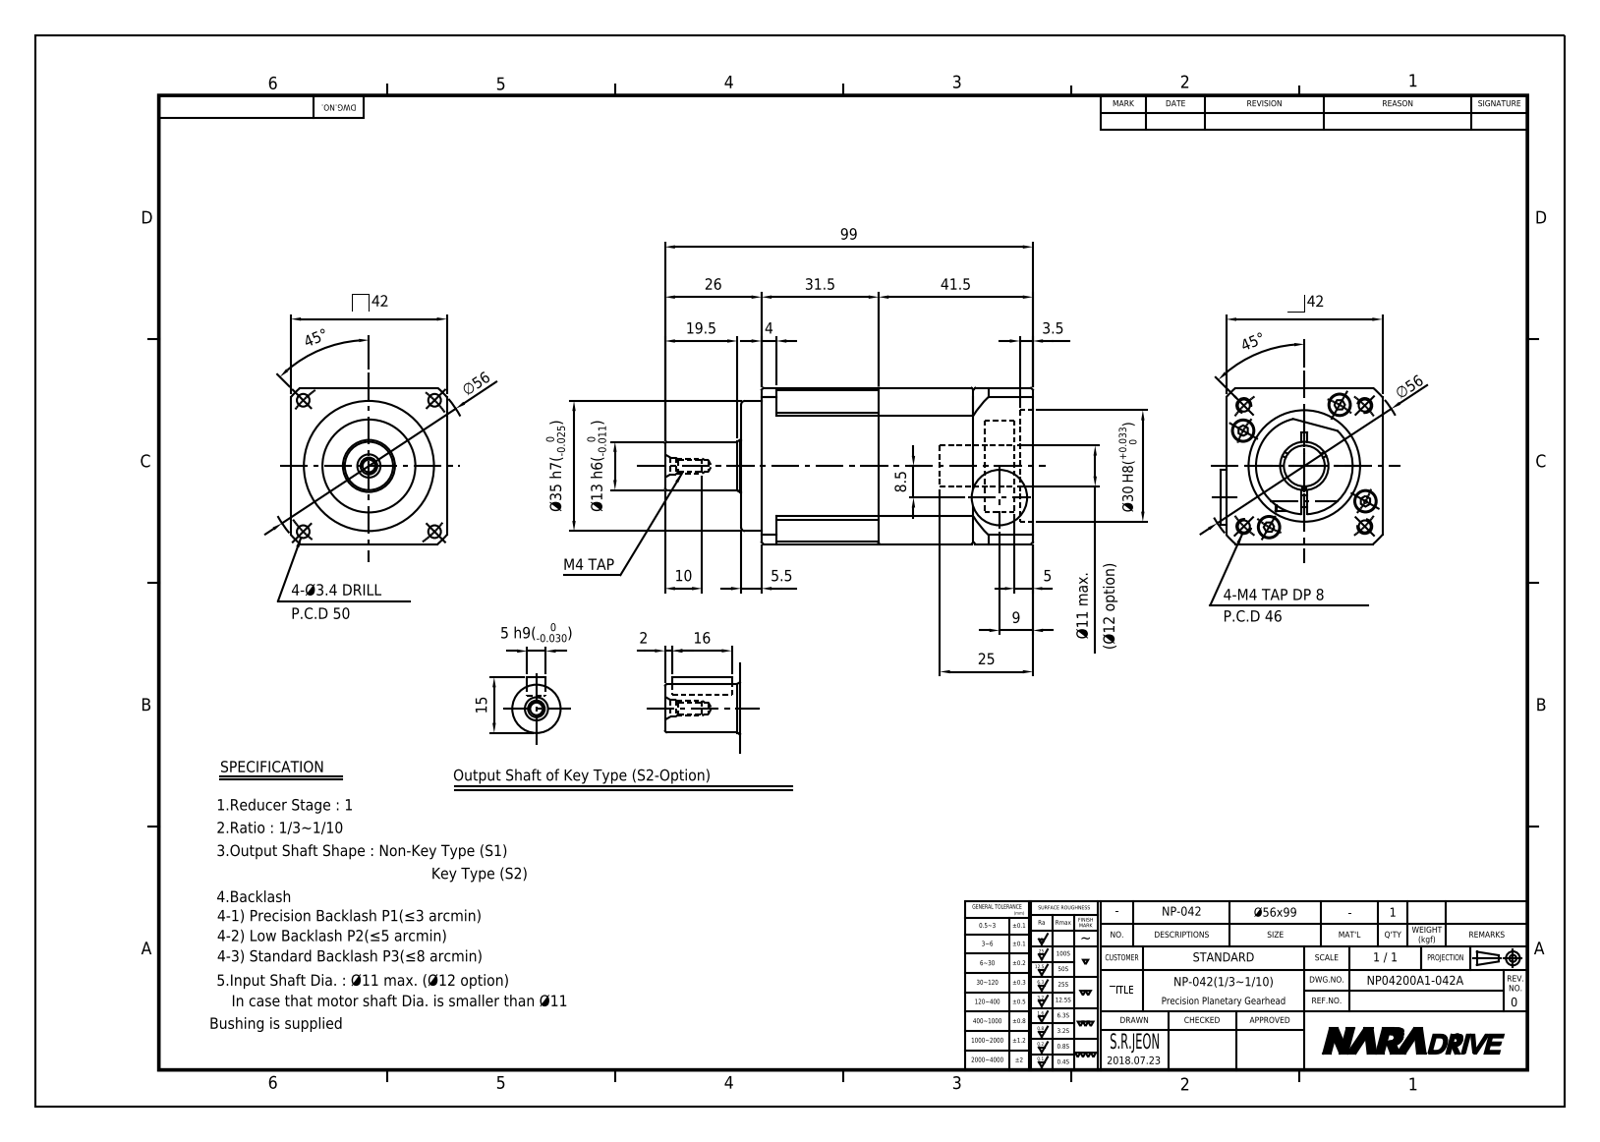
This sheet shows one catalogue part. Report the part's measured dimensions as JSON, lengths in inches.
{"part_name": "NP04200A1-042A-S1", "step_written_by": "Autodesk Inventor 2015 (AUTOMOTIVE_DESIGN)", "units": "inches", "bodies": {"solids": 2, "faces": 332, "planar": 161, "cylindrical": 90, "other": 81}, "overall_size": [3.898, 1.713, 1.654], "volume_in3": 5.967, "surface_area_in2": 44.7, "round_holes": [[0.134, 13], [0.097, 9], [0.236, 8], [0.128, 5], [0.177, 1], [0.276, 1], [0.335, 1], [0.433, 1], [0.512, 1], [1.063, 1], [1.102, 1], [1.181, 1]], "round_bosses_or_shafts": [[0.217, 5], [0.118, 5], [1.378, 1], [1.024, 1], [0.984, 1], [0.591, 1], [0.551, 1], [0.315, 1]], "partial_cylinders_radius": [[0.197, 4], [0.118, 1], [0.984, 1], [1.102, 1]], "face_to_face_distances": [1.654, 1.004, 2.874, 1.87, 0.217, 1.22, 3.091, 0.197, 1.24, 0.315], "hole_center_spacings": [0.214, 0.326, 0.748, 0.984, 1.071, 1.074, 1.155, 1.281]}
